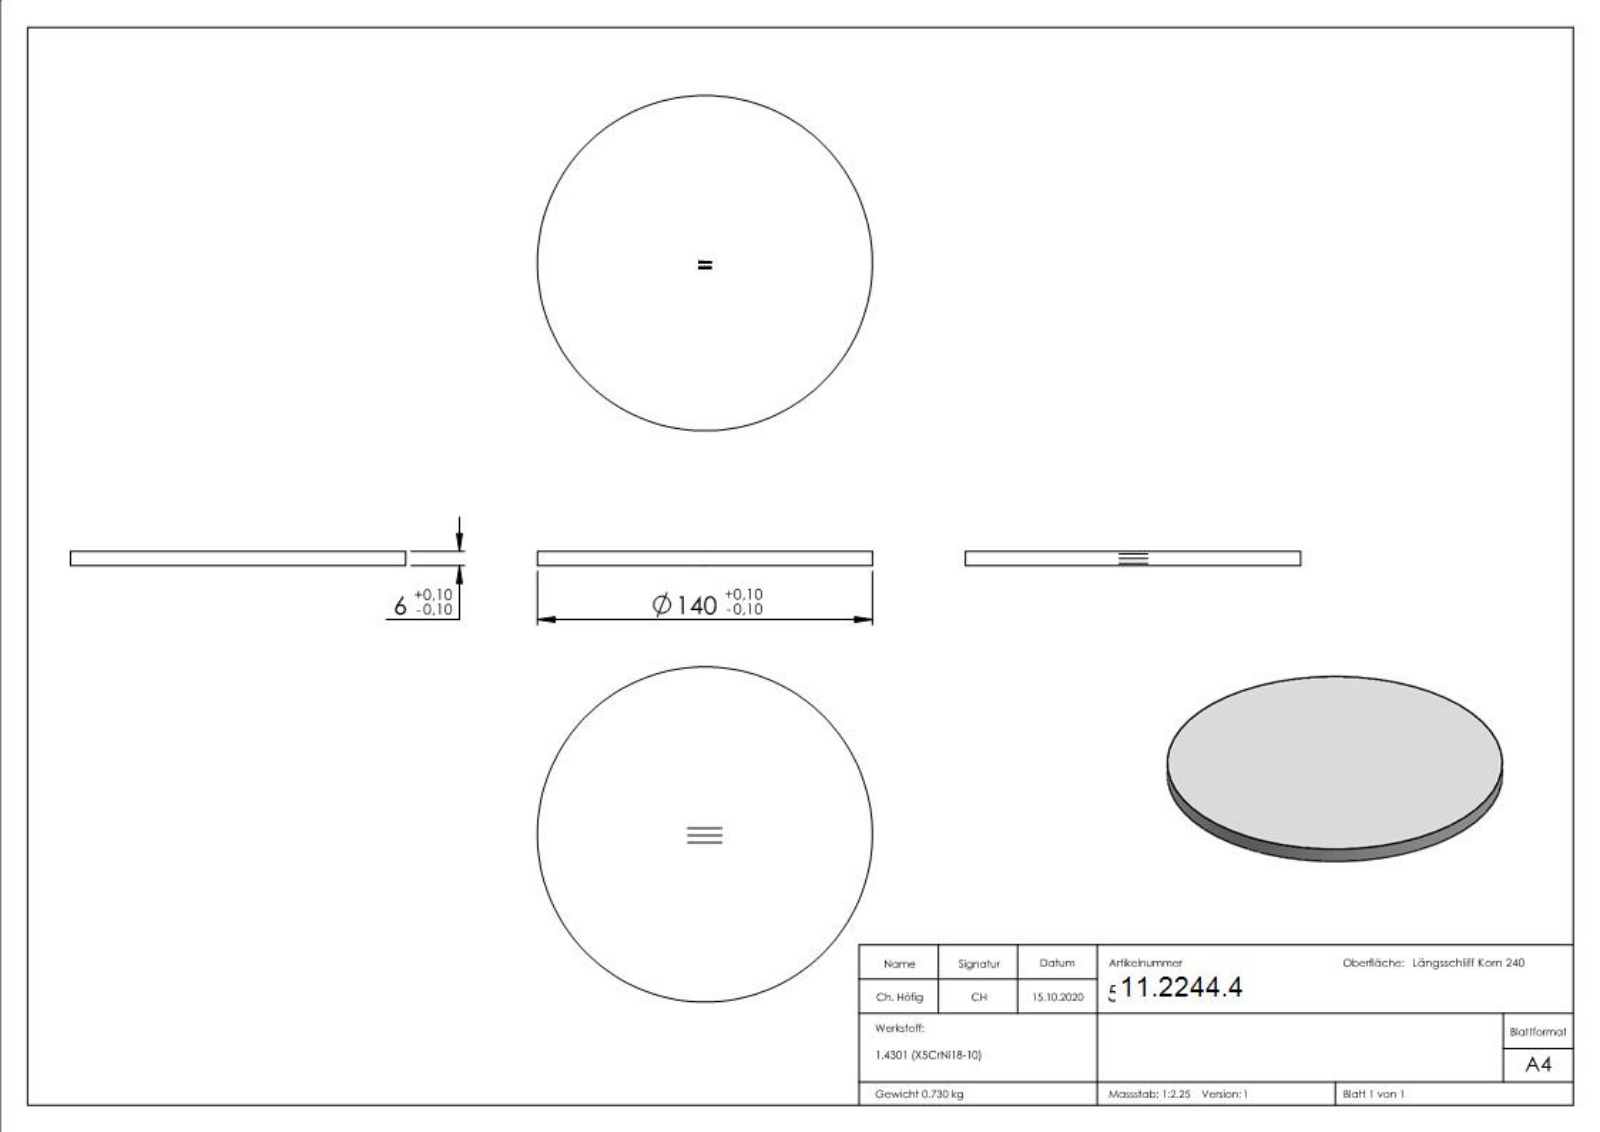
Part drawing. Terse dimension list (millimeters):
name: 53140-240
written by: SolidWorks 2018 (CONFIG_CONTROL_DESIGN)
unit: mm
bodies: 1 solid, 227 faces (131 planar, 2 cylindrical, 94 other)
size: 140 × 140 × 6
volume: 92 363 mm³; area: 33 432 mm²
bosses: 1× ⌀140
face distances: 6, 5.9, 2.2, 2.18, 0.83, 0.74, 2.61, 1.78, 2.54, 0.76
